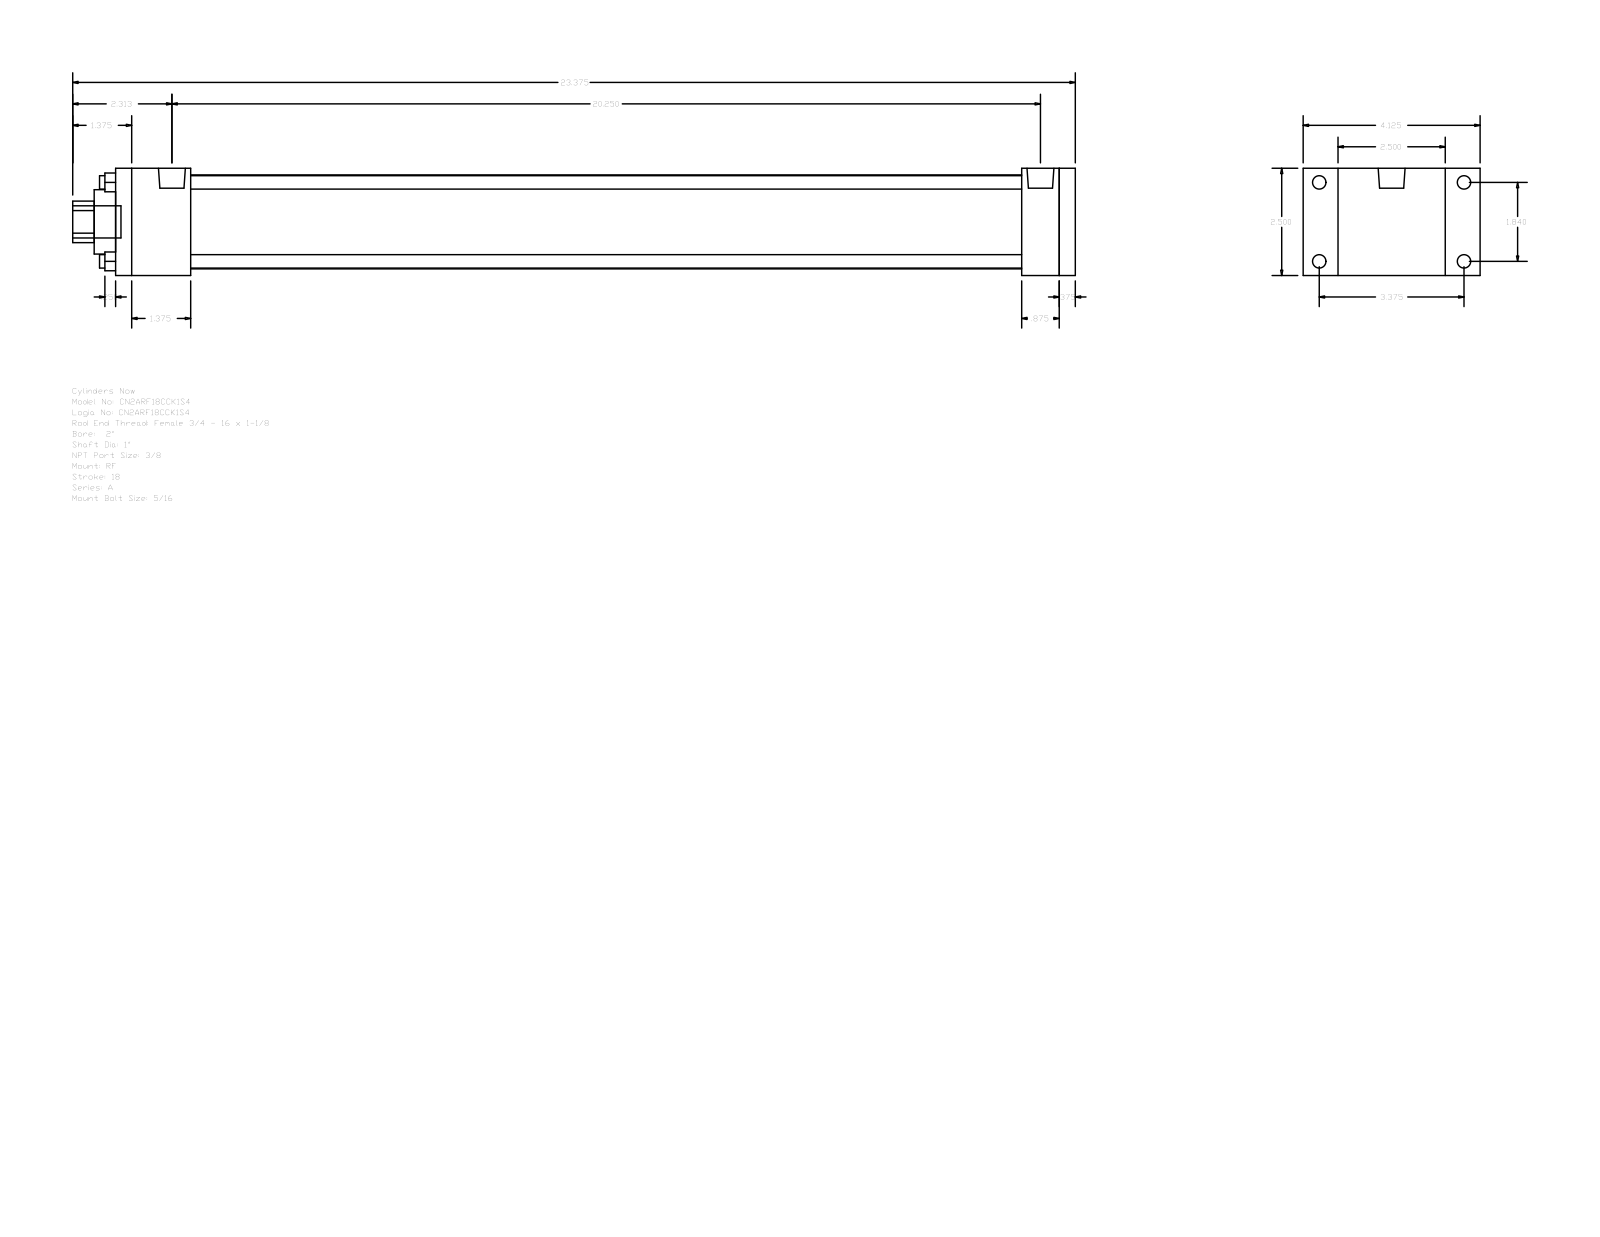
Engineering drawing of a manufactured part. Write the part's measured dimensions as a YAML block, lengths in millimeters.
part_name: "A_RF__0200_1"
step_written_by: "GSSL Pune (CONFIG_CONTROL_DESIGN)"
units: millimeters
bodies: {solids: 0, faces: 92, planar: 64, cylindrical: 28, other: 0}
overall_size: [593.73, 104.78, 63.5]
round_holes:
  - {diameter: 7.94, count: 4}
  - {diameter: 25.4, count: 1}
  - {diameter: 38.1, count: 1}
  - {diameter: 55.63, count: 1}
round_bosses_or_shafts:
  - {diameter: 7.94, count: 4}
  - {diameter: 5.56, count: 4}
  - {diameter: 15.93, count: 2}
  - {diameter: 19.05, count: 1}
partial_cylinders:
  - {radius: 12.29, count: 1}
face_to_face_distances: [63.5, 9.53, 568.33, 558.8, 20.64, 44.45, 514.35, 523.88, 536.58, 492.13]
hole_center_spacings: [33.05, 46.74, 66.1]
